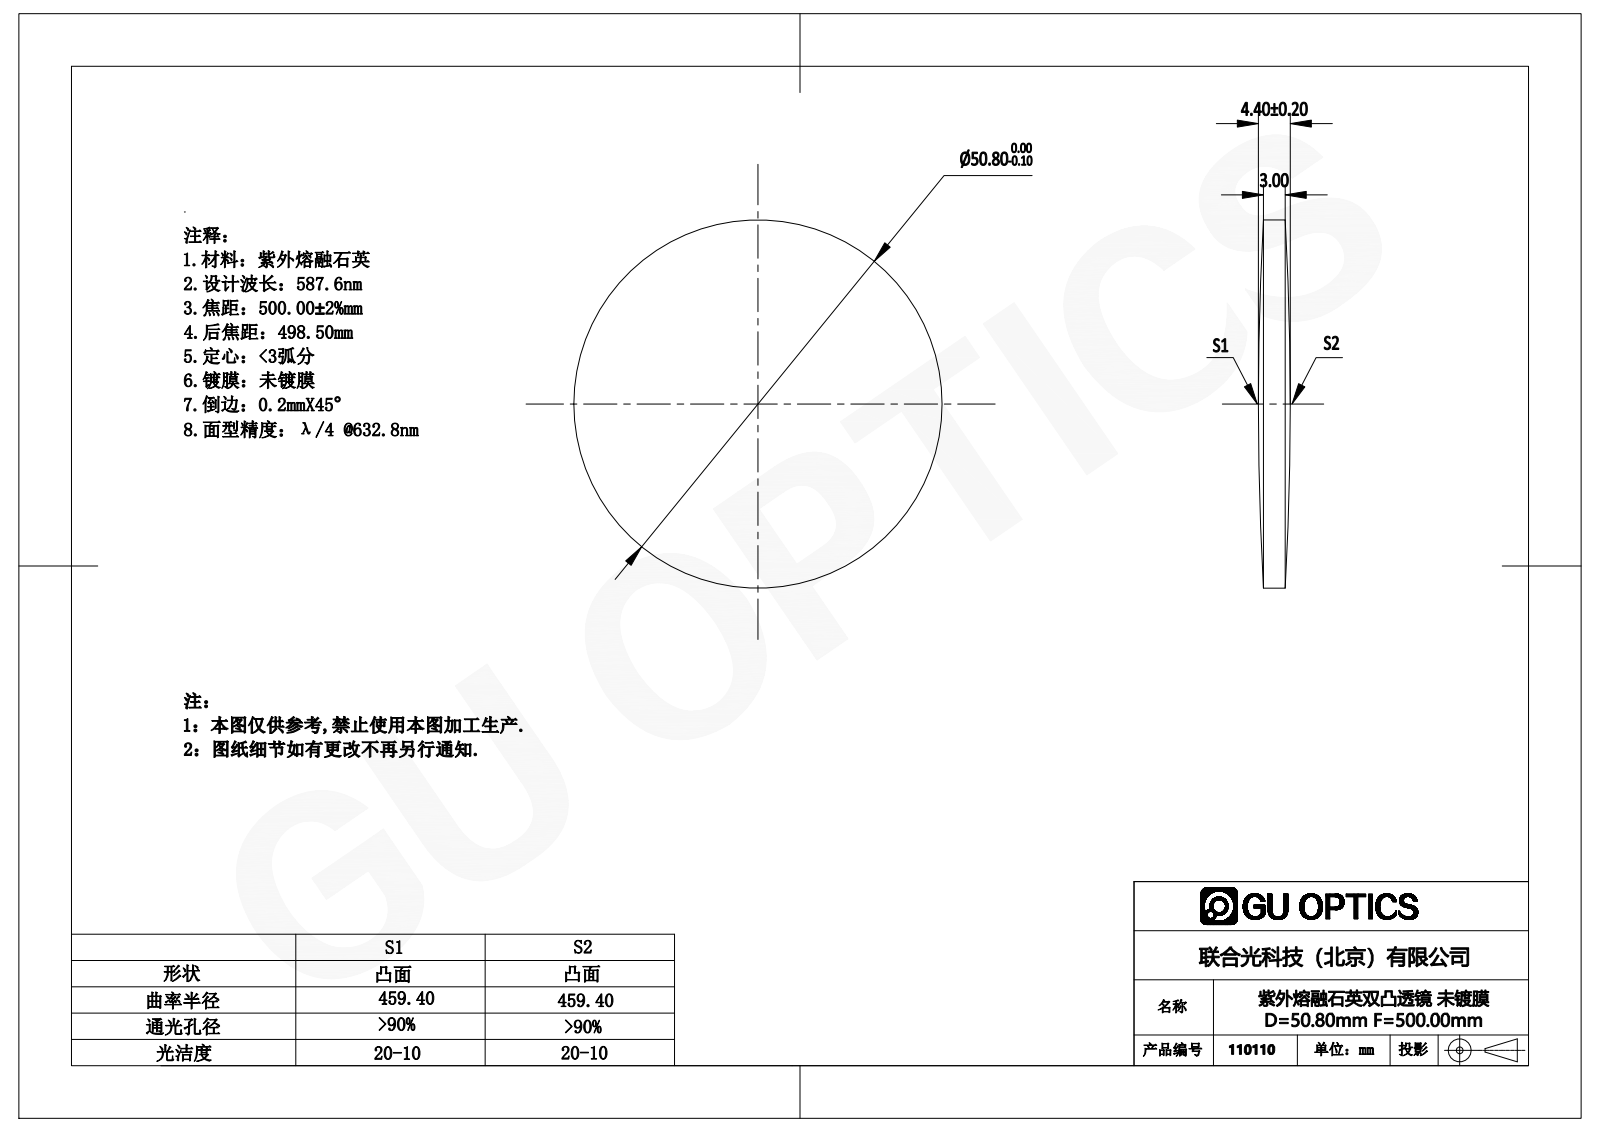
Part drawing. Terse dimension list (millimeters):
name: 110110
written by: SolidWorks 2016 (CONFIG_CONTROL_DESIGN)
unit: mm
bodies: 1 solid, 6 faces (0 planar, 2 cylindrical, 4 other)
size: 50.8 × 50.8 × 4.4
volume: 7 500 mm³; area: 4 536 mm²
bosses: 1× ⌀50.8
